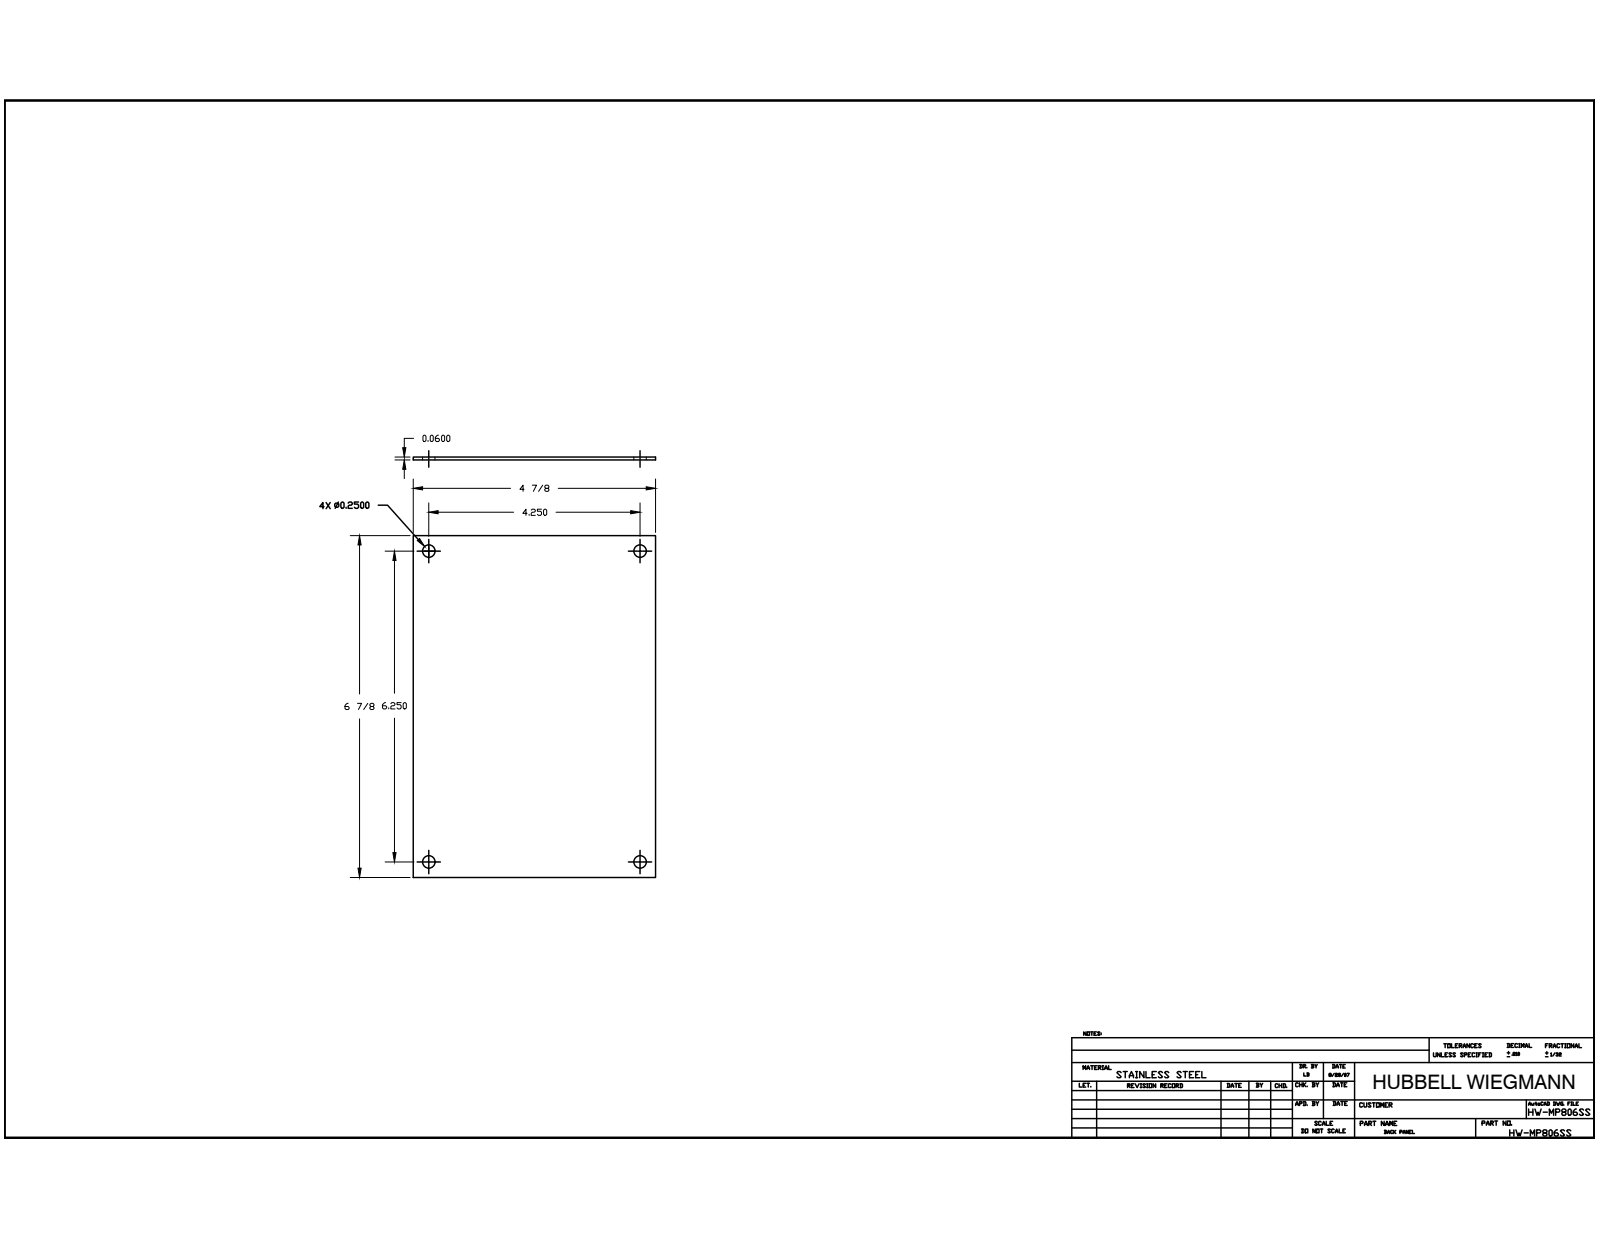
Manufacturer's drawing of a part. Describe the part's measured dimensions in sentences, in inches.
The part is named "BP86SS_STP". Its 3-D file was written by "Autodesk Inventor 2014 (AUTOMOTIVE_DESIGN)". It is 1 solid with 10 faces: 6 planar, 4 cylindrical and 0 other. Overall it measures 6.875 by 4.875 by 0.06 inches. Its volume is 1.999 cubic inches and its surface area 68.24 square inches. Round holes: 4 of diameter 0.25. The main face-to-face distances are 0.06, 4.875, 6.875. The hole center spacings are 4.25, 6.25, 7.558.
